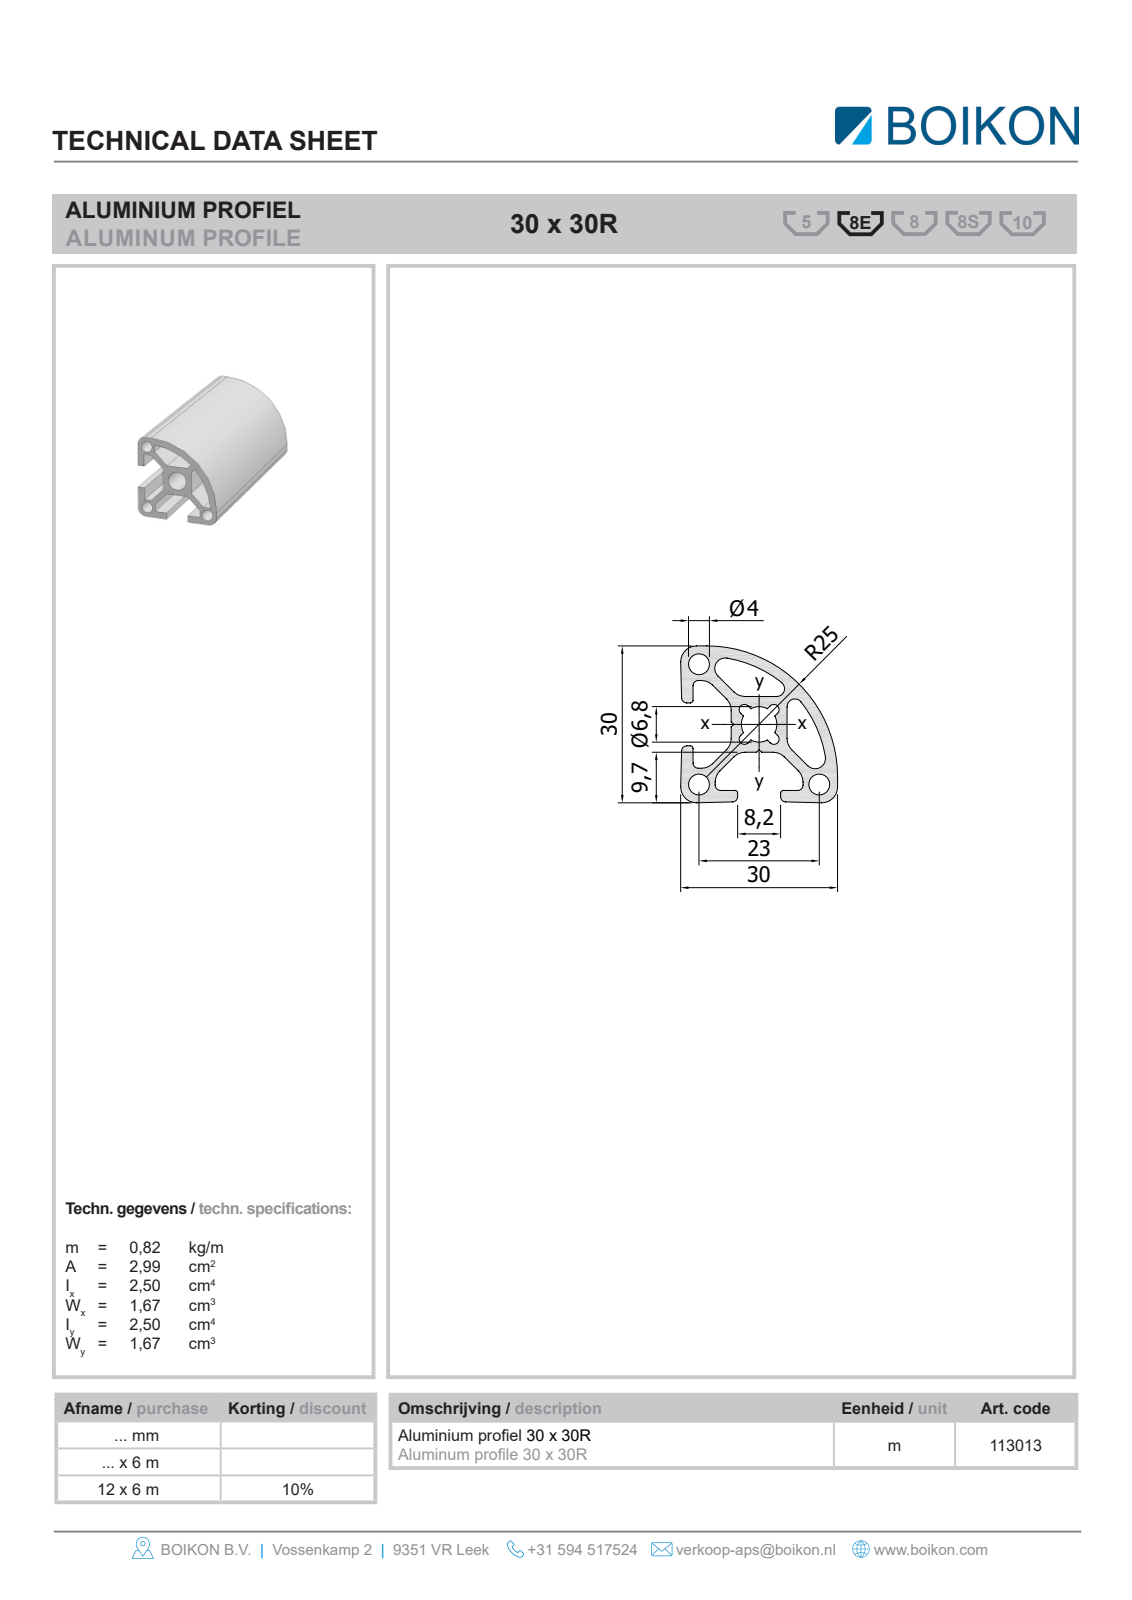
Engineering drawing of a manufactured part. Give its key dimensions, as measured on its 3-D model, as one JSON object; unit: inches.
{"part_name": "Root; 11301330x30-RBOIKON0", "step_written_by": "HiCAD 2013 1802.4 Build 509 (AUTOMOTIVE_DESIGN)", "units": "inches", "bodies": {"solids": 1, "faces": 44, "planar": 34, "cylindrical": 10, "other": 0}, "overall_size": [39.37, 1.181, 1.181], "volume_in3": 19.36, "surface_area_in2": 461.3, "round_holes": [[0.157, 3], [0.268, 1]], "partial_cylinders_radius": [[0.118, 3], [0.891, 1], [0.984, 1]], "face_to_face_distances": [0.079, 0.799, 0.382, 0.094, 0.705, 0.287, 0.417, 0.13, 0.547, 0.252], "hole_center_spacings": [0.64, 0.906, 1.281]}
